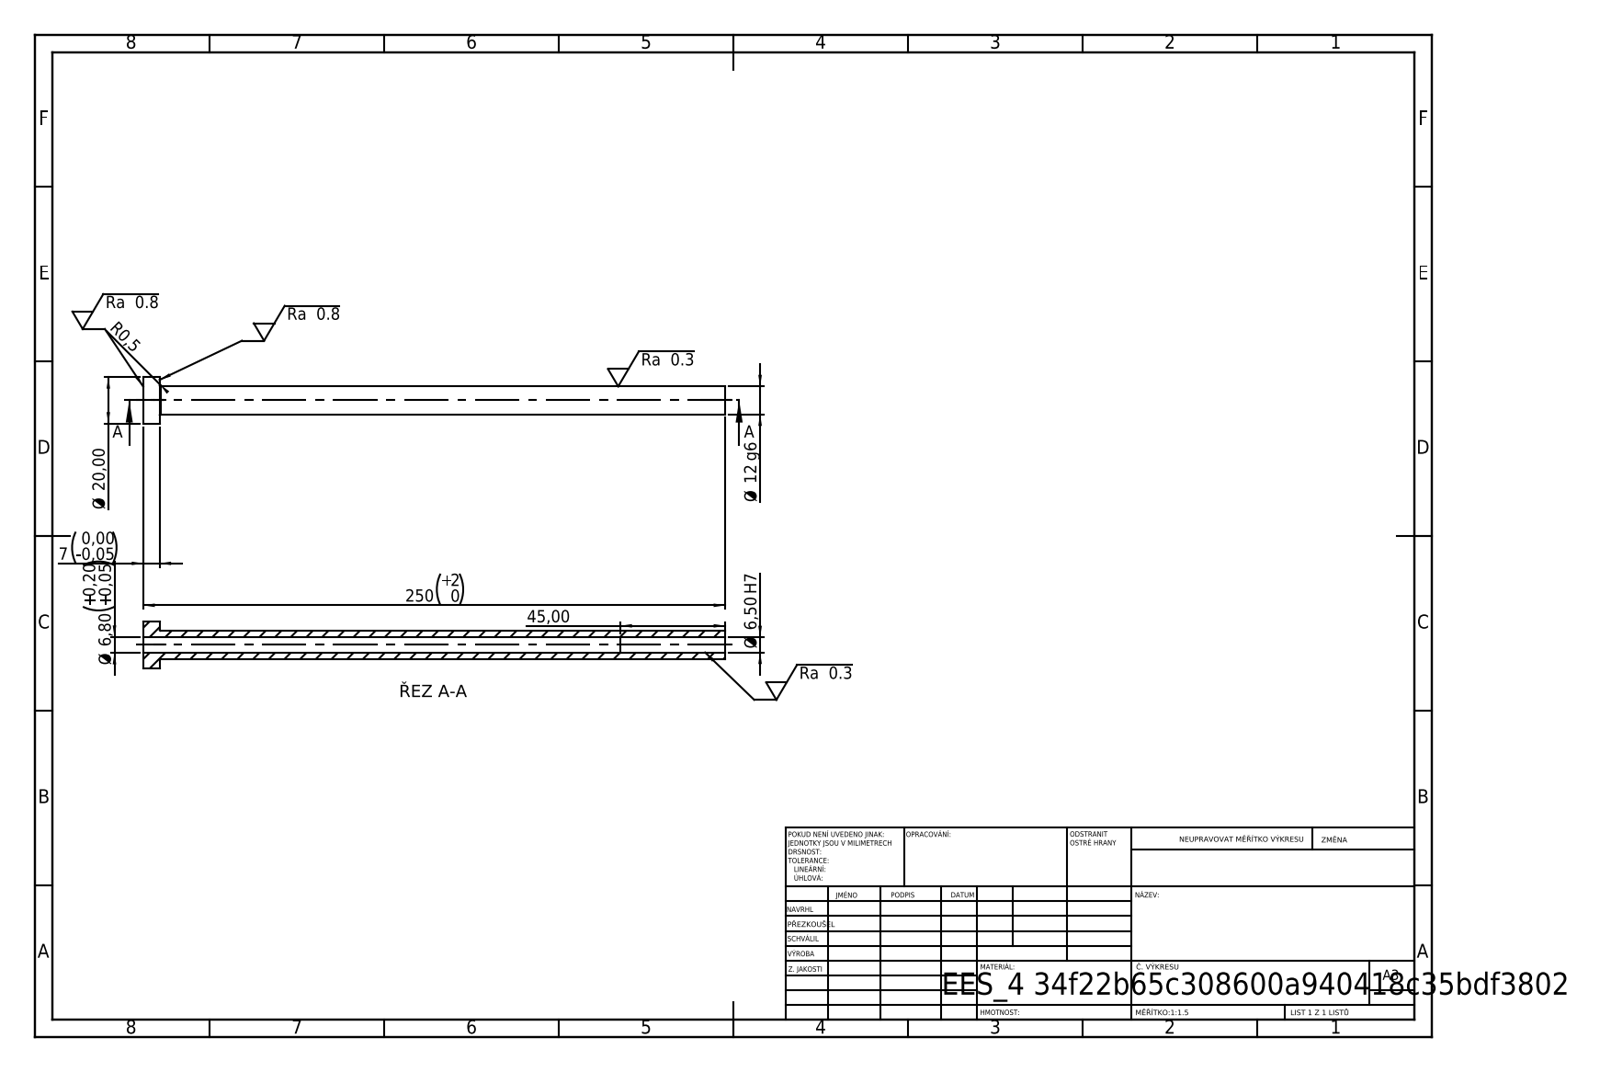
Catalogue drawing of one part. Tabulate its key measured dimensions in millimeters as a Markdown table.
| quantity | value |
| --- | --- |
| STEP written by | SolidWorks 2019 (CONFIG_CONTROL_DESIGN) |
| units | millimeters |
| bodies | 1 solid, 14 faces (4 planar, 8 cylindrical, 2 other) |
| overall size | 250 × 20 × 20 |
| volume | 20 746 mm³ |
| surface area | 15 453 mm² |
| round holes (diameter × count) | 6.5 × 1, 6.8 × 1 |
| round bosses / shafts (diameter × count) | 20 × 1, 12 × 1 |
| main face-to-face distances | 7, 250, 243, 205, 198, 45 |
